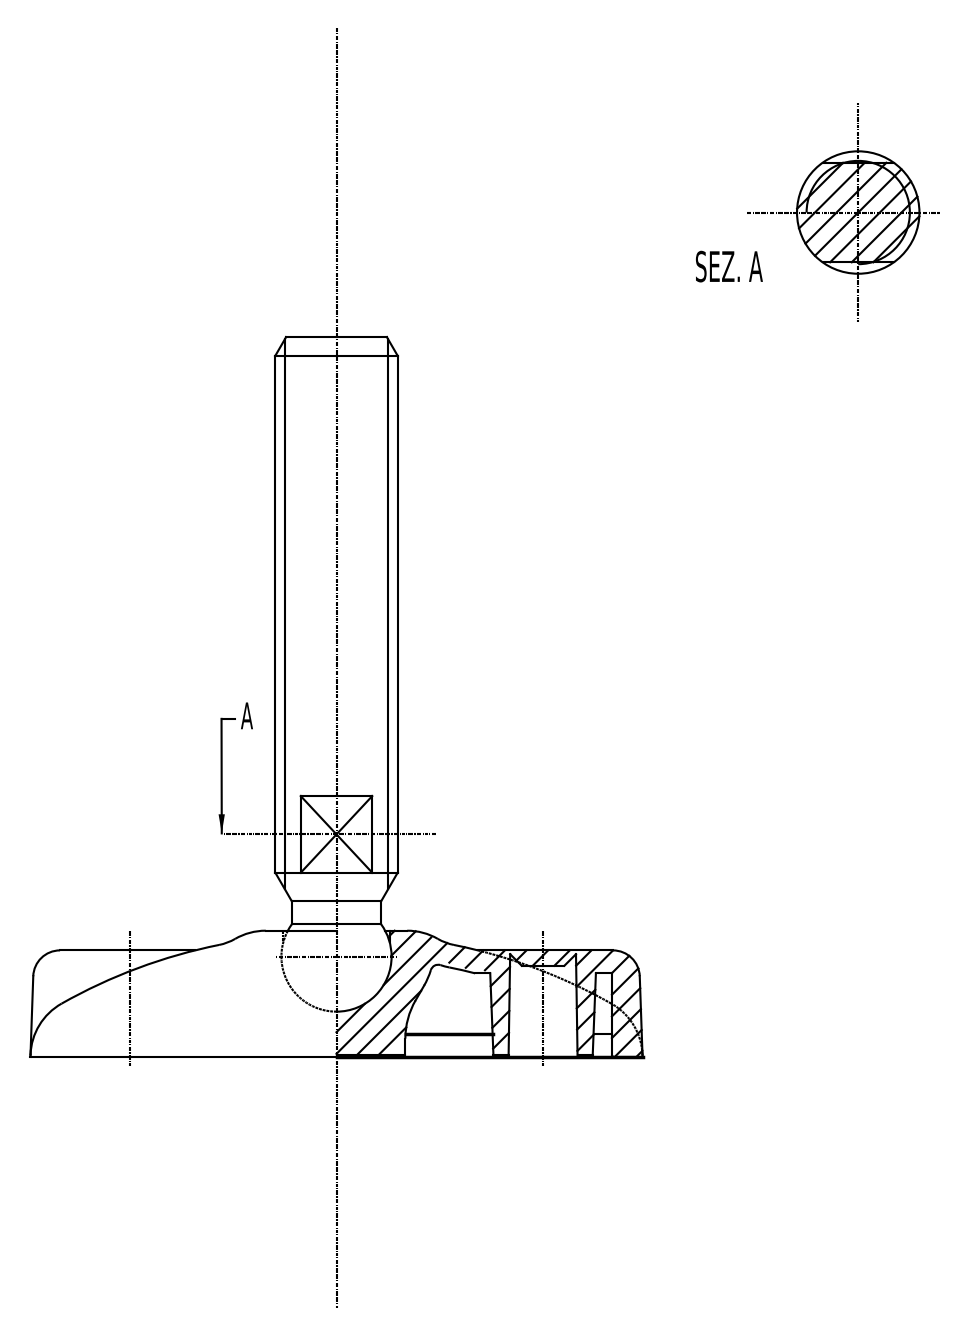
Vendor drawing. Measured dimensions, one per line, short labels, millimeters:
name: 440000009286; 440000009285; CPDSN0000039
written by: Autodesk Inventor 2016 (AUTOMOTIVE_DESIGN)
unit: mm
bodies: 2 solids, 51 faces (13 planar, 12 cylindrical, 26 other)
size: 94.84 × 80 × 80
volume: 70 922 mm³; area: 18 023 mm²
holes: 2× ⌀9, 1× ⌀13.42, 1× ⌀16.97
bosses: 1× ⌀16, 1× ⌀11.7
rounds: 4× R2, 2× R10.27
face distances: 14, 94.84, 80.84, 13, 32.34, 18.34, 62.5, 17.5, 3.5, 14.84
hole spacings: 27, 54
